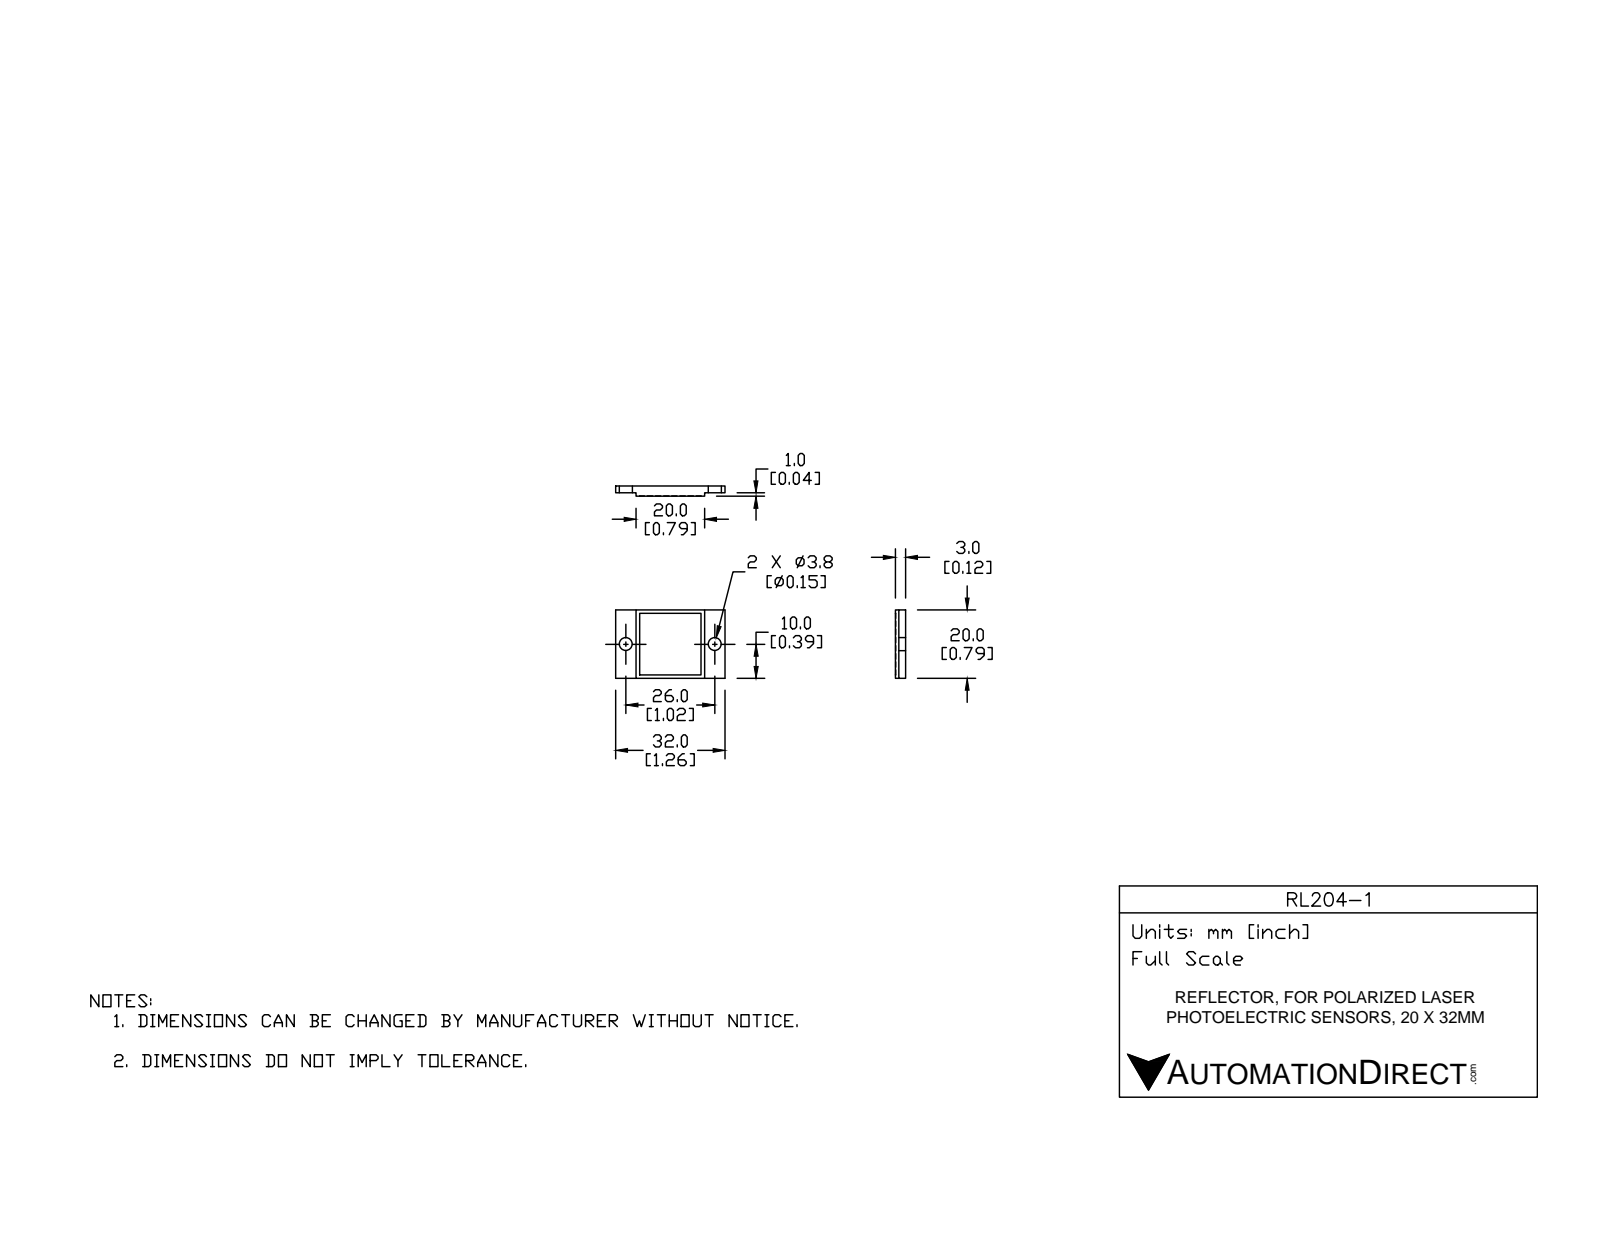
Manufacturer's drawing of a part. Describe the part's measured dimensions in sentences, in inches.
The part is named "RL-204-1". Its 3-D file was written by "SolidWorks 2017 (AUTOMOTIVE_DESIGN)". It is 1 solid with 19 faces: 15 planar, 4 cylindrical and 0 other. Overall it measures 1.26 by 0.787 by 0.118 inches. Its volume is 0.098 cubic inches and its surface area 2.445 square inches. Round holes: 2 of diameter 0.15. The main face-to-face distances are 0.114, 0.079, 0.035, 0.787, 0.039, 0.118, 0.236, 1.024, 1.26, 0.748. The hole center spacings are 1.024.
